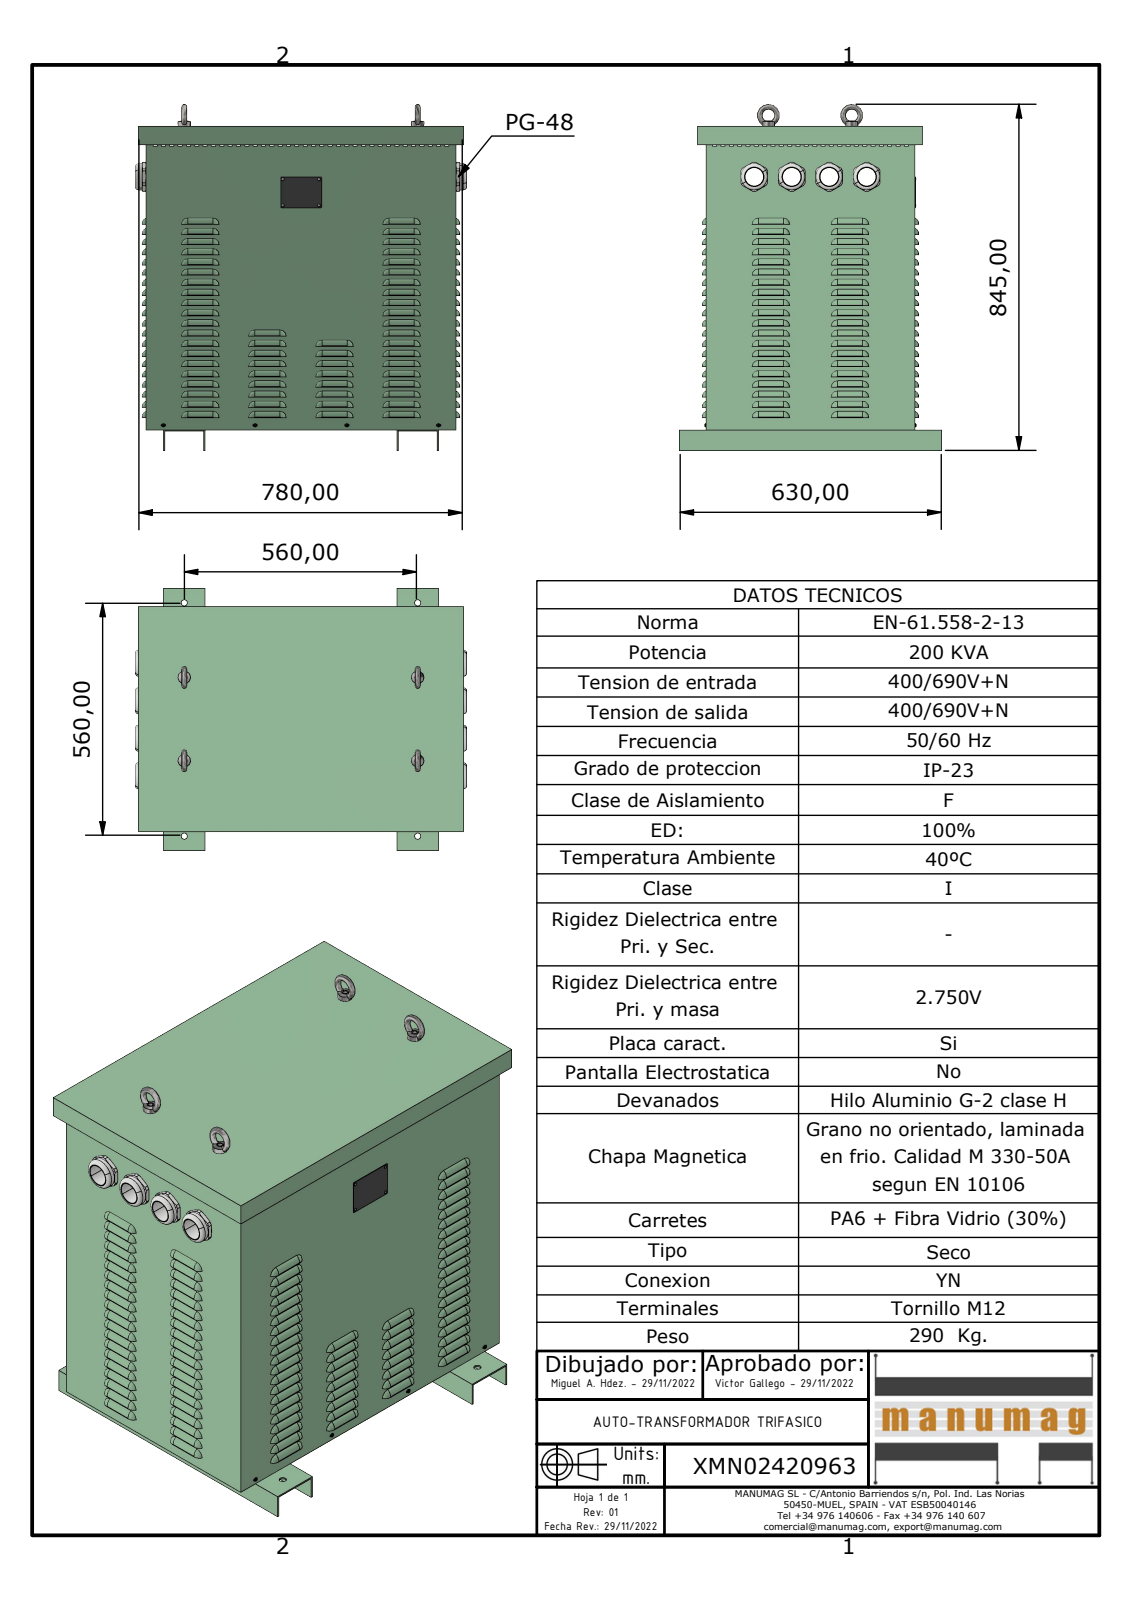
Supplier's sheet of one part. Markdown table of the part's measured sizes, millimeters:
| quantity | value |
| --- | --- |
| part name | XMN02420963; JE200 CUERPO; JE160 EXPORT JE200 EXPORT NACIONAL BASE; JE160 EXPORT JE200 EXPORT NACIONAL PATA (+6 more) |
| STEP written by | Autodesk Inventor 2023 (AUTOMOTIVE_DESIGN) |
| units | millimeters |
| bodies | 30 solids, 4663 faces (1571 planar, 1992 cylindrical, 1100 other) |
| overall size | 835 × 795.27 × 630 |
| volume | 7 588 000 mm³ |
| surface area | 6 374 000 mm² |
| round holes (diameter × count) | 11 × 936, 15 × 12, 4 × 4, 5 × 4, 10.11 × 4, 44 × 4, 60 × 4 |
| round bosses / shafts (diameter × count) | 63 × 4, 59.3 × 4, 59.15 × 4, 57.63 × 4, 30 × 4, 4 × 4, 3.62 × 4, 3.2 × 4 |
| partial cylindrical surfaces (radius × count) | 14 × 194, 7 × 80, 15 × 80, 2.5 × 8, 2 × 4, 35 × 4 |
| main face-to-face distances | 2, 500, 730, 742, 498, 502, 732, 740, 728, 744 |
| hole center spacings | 15, 30, 33.54, 204.55, 159.71, 204, 129.87, 159 |
